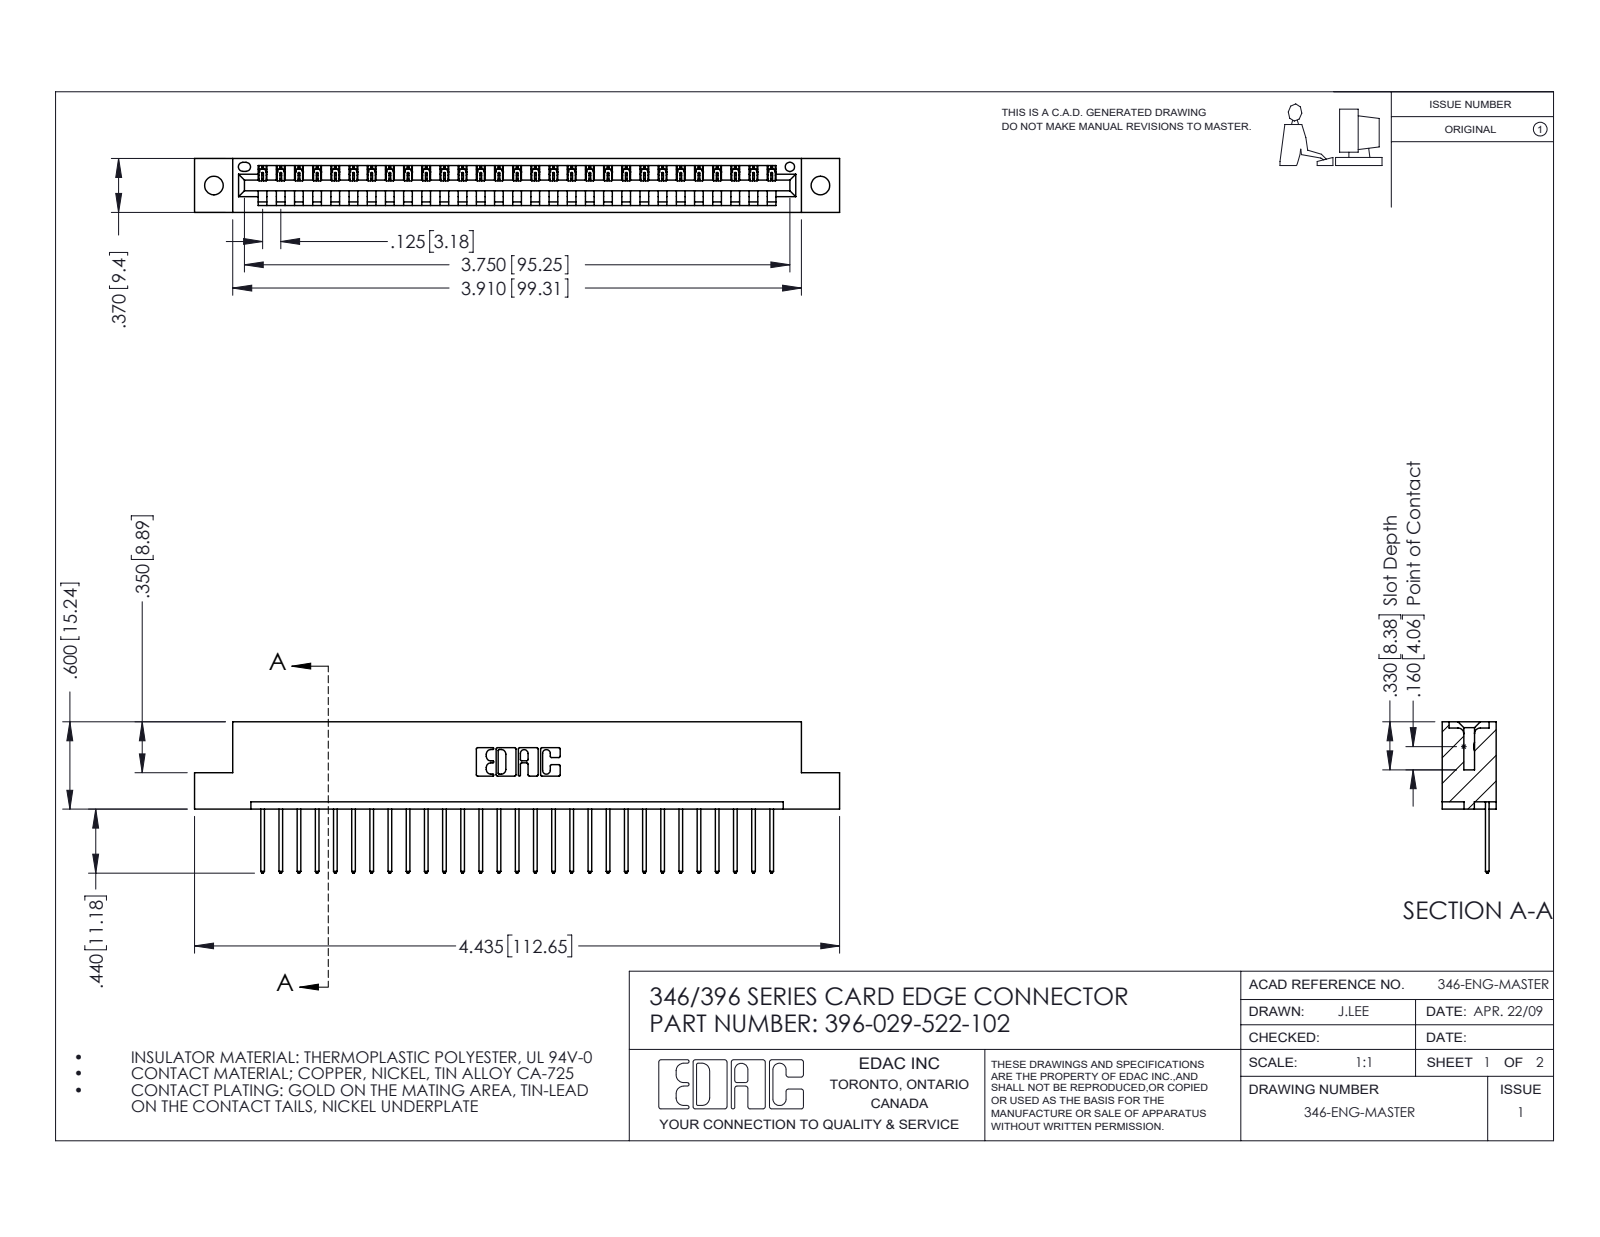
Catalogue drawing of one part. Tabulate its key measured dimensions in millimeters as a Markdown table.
| quantity | value |
| --- | --- |
| part name | 396-029-522-102; 345-292-001_345-293-122; 346 Part_Flush Mounting Lugs - 0.128 Dia |
| STEP written by | SolidWorks 2016 (CONFIG_CONTROL_DESIGN) |
| units | millimeters |
| bodies | 30 solids, 1804 faces (1236 planar, 568 cylindrical, 0 other) |
| overall size | 112.6 × 26.4 × 9.4 |
| volume | 10 700 mm³ |
| surface area | 13 020 mm² |
| round holes (diameter × count) | 3.3 × 2, 1.6 × 1 |
| partial cylindrical surfaces (radius × count) | 0.2 × 58, 0.3 × 58, 0.3 × 22, 0.2 × 6, 0.8 × 6, 0.7 × 3, 0.8 × 2, 1 × 2 |
| main face-to-face distances | 1.2, 8.2, 6.4, 9.4, 1.8, 7.6, 0.6, 3.8, 5.6, 2.5 |
| hole center spacings | 6.2, 100.6, 105.9 |
